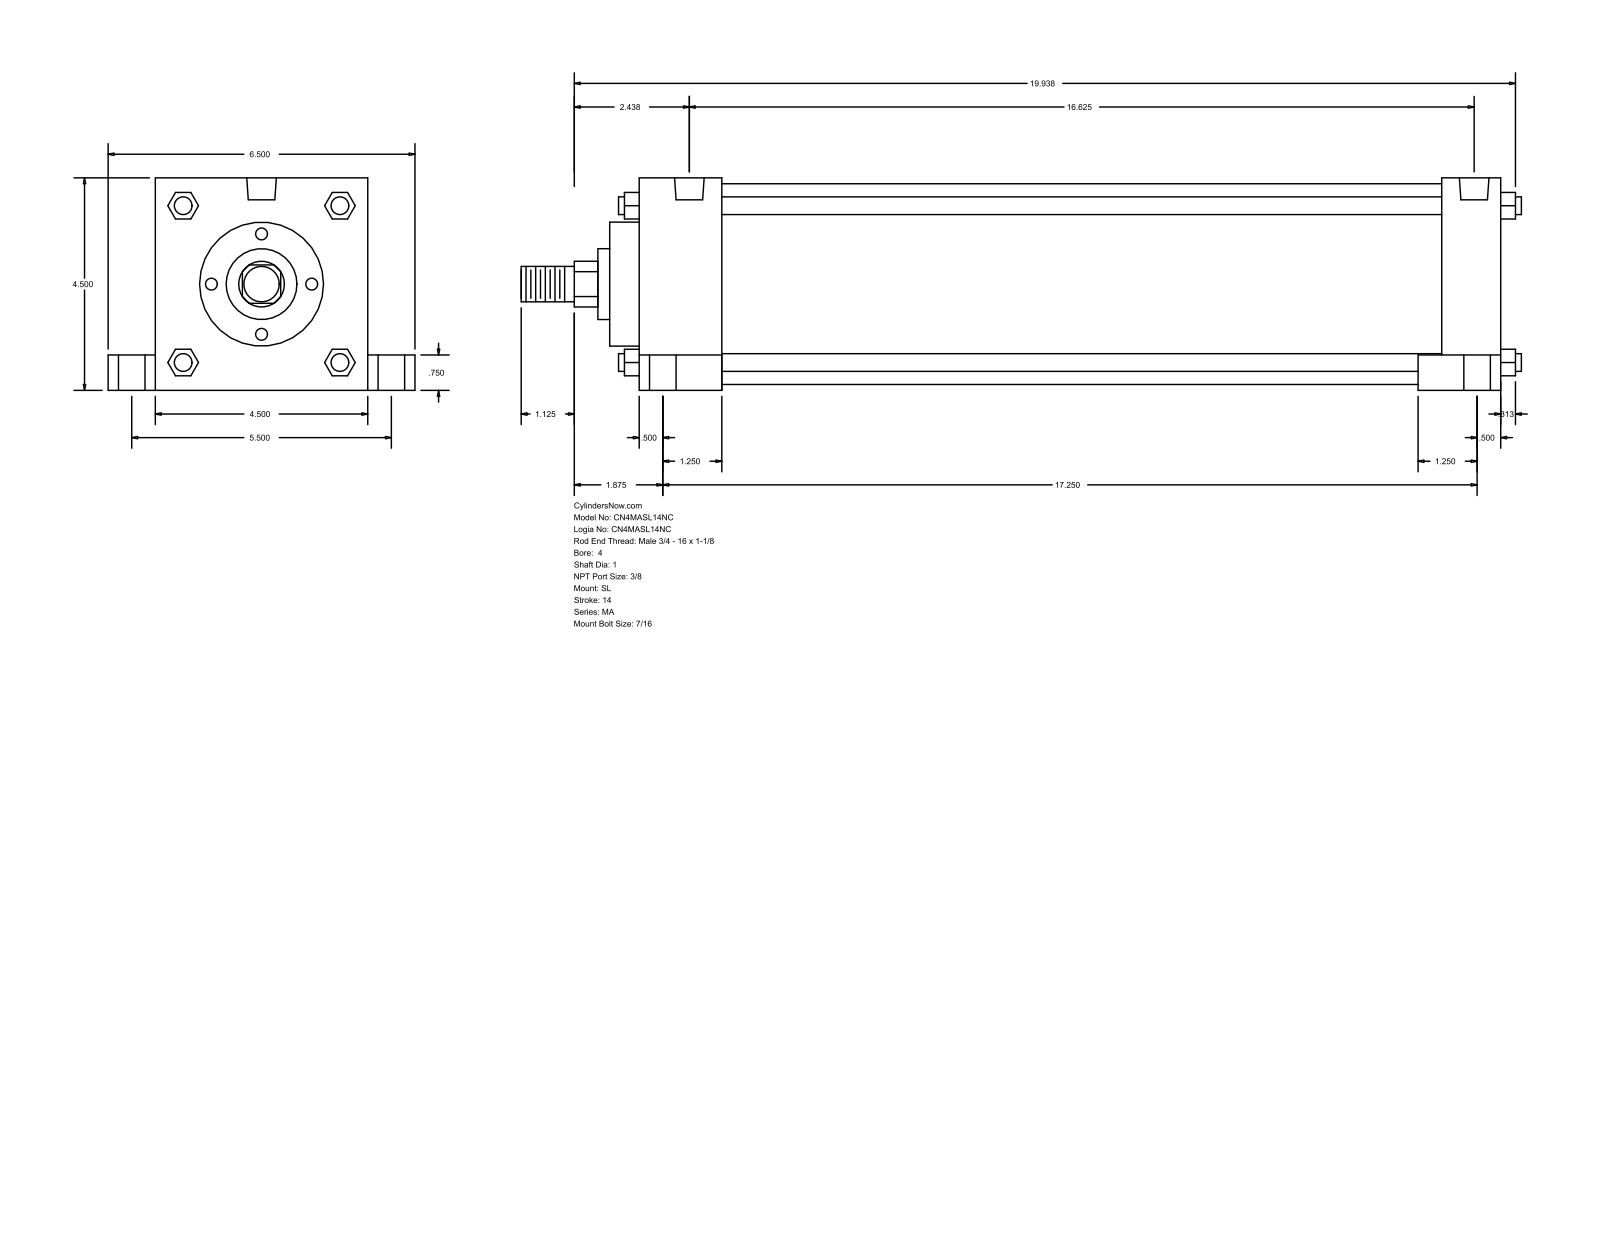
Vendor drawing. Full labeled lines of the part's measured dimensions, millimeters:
Part name (STEP PRODUCT): MA_SL__0400_1
STEP written by: GSSL Pune (CONFIG_CONTROL_DESIGN)
Units: millimetres
Bodies: 0 solids, 150 faces (113 planar, 37 cylindrical, 0 other)
Overall size (bounding box): 538.16 × 165.1 × 114.3
Round holes (diameter × count): ⌀11.11 ×4, ⌀14.29 ×4, ⌀20.64 ×4, ⌀15.93 ×2
Round bosses / shafts (diameter × count): ⌀9.53 ×4, ⌀107.95 ×1, ⌀66.67 ×1, ⌀38.1 ×1, ⌀25.4 ×1, ⌀19.05 ×1
Partial cylindrical surfaces — rounded edges, fillets, slot ends (radius × count): R12.29 ×1
Main face-to-face distances: 114.3, 463.56, 387.35, 44.46, 419.1, 431.81, 31.75, 25.4, 139.7, 19.05
Hole centre spacings: 4.76, 69.87, 70.14, 71.3, 72.4, 139.7, 412.76, 417.52
